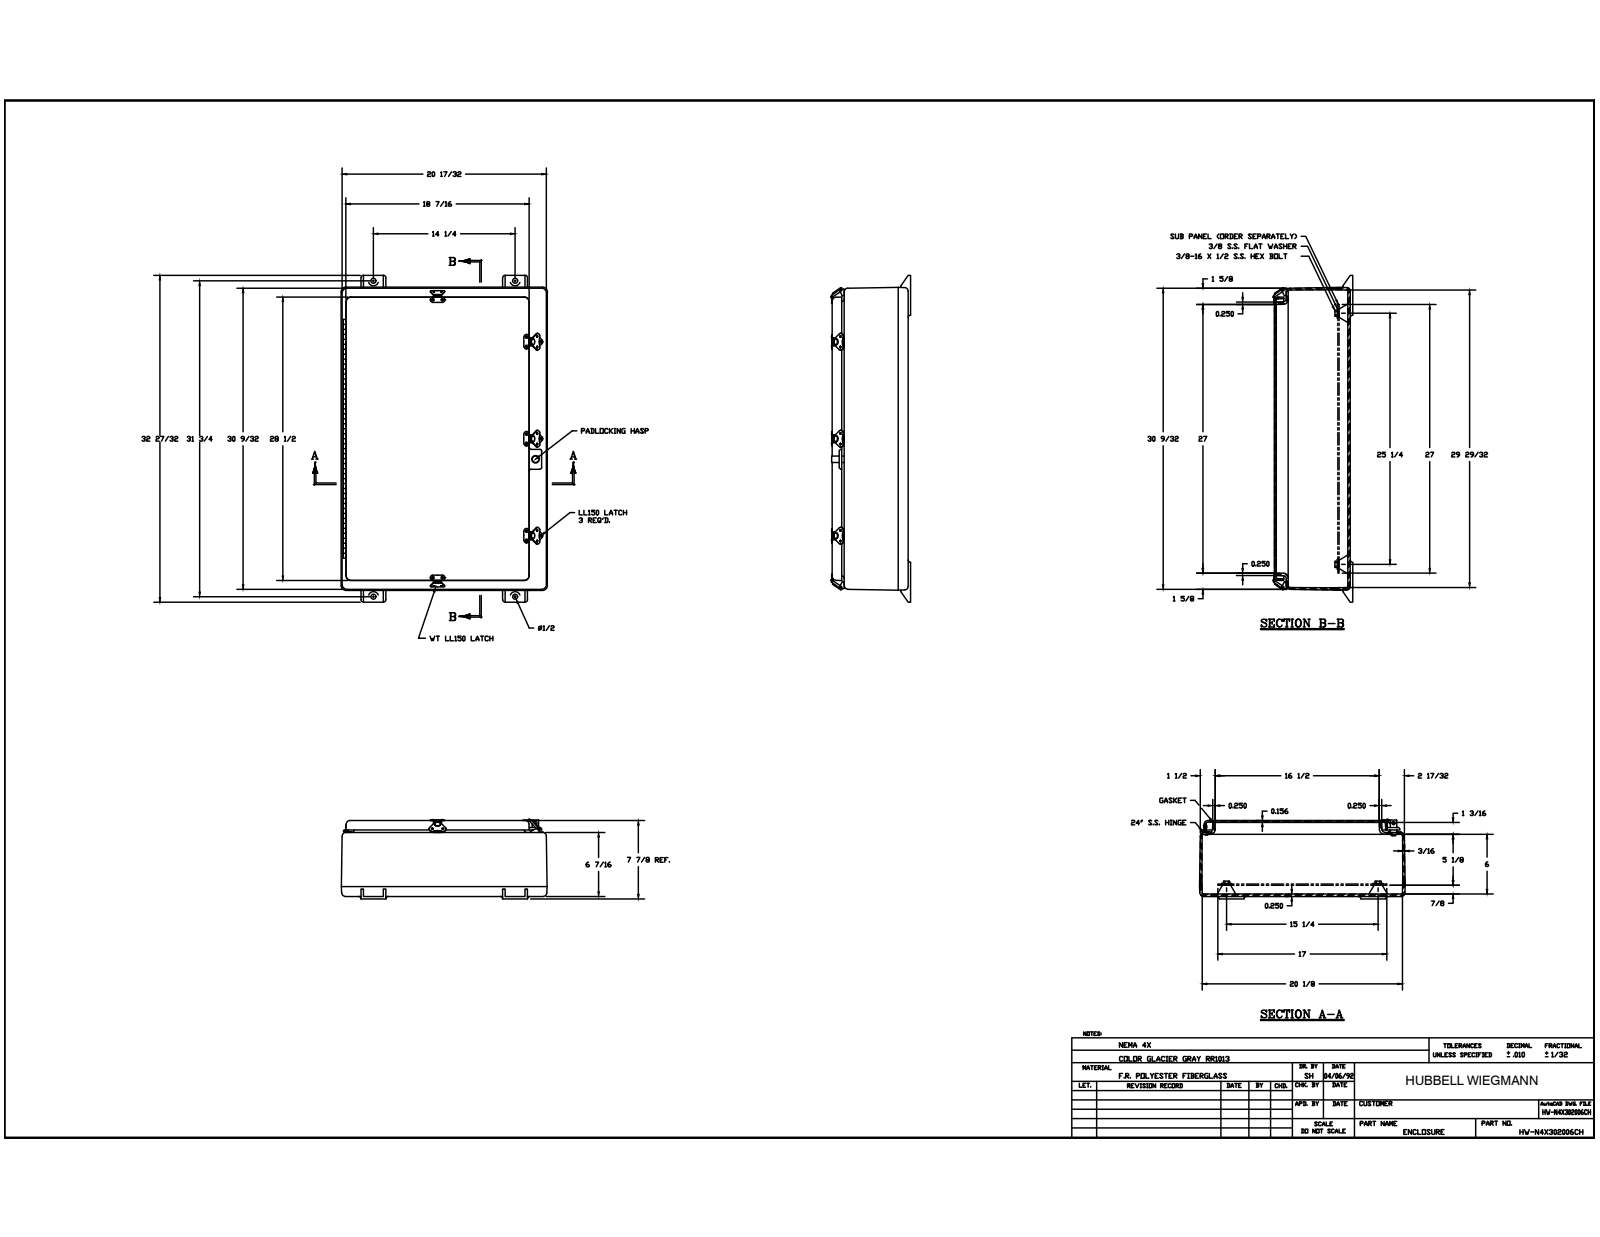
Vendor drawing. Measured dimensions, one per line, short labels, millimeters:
name: WPN30206SHWT; WPN3020B; WPN30206HWTPCVR; N30206G (+8 more)
written by: Autodesk Inventor 2014 (AUTOMOTIVE_DESIGN)
unit: mm
bodies: 63 solids, 1702 faces (646 planar, 690 cylindrical, 366 other)
size: 834.23 × 527.05 × 209.31
volume: 7 227 000 mm³; area: 3 013 000 mm²
holes: 37× ⌀3.3, 20× ⌀1.59, 10× ⌀3.5, 10× ⌀4.76, 8× ⌀1.65, 4× ⌀14.3, 3× ⌀3.43, 3× ⌀3.97, 2× ⌀12.95, 2× ⌀12.96, 1× ⌀3.17, 1× ⌀5.11
bosses: 20× ⌀3.56, 8× ⌀7.54, 5× ⌀12.7, 3× ⌀5.08, 1× ⌀6.35, 1× ⌀5.11
rounds: 127× R0.25, 29× R4.76, 21× R9.53, 20× R0.76, 20× R6.35, 19× R7.94, 12× R12.7, 10× R1.59
face distances: 6.35, 3.96, 4.76, 189.71, 183.36, 187.32, 193.67, 1.59, 3.17, 30.16
hole spacings: 247.65, 190.5, 393.7, 25.4, 81.56, 248.38, 383.21, 495.3
